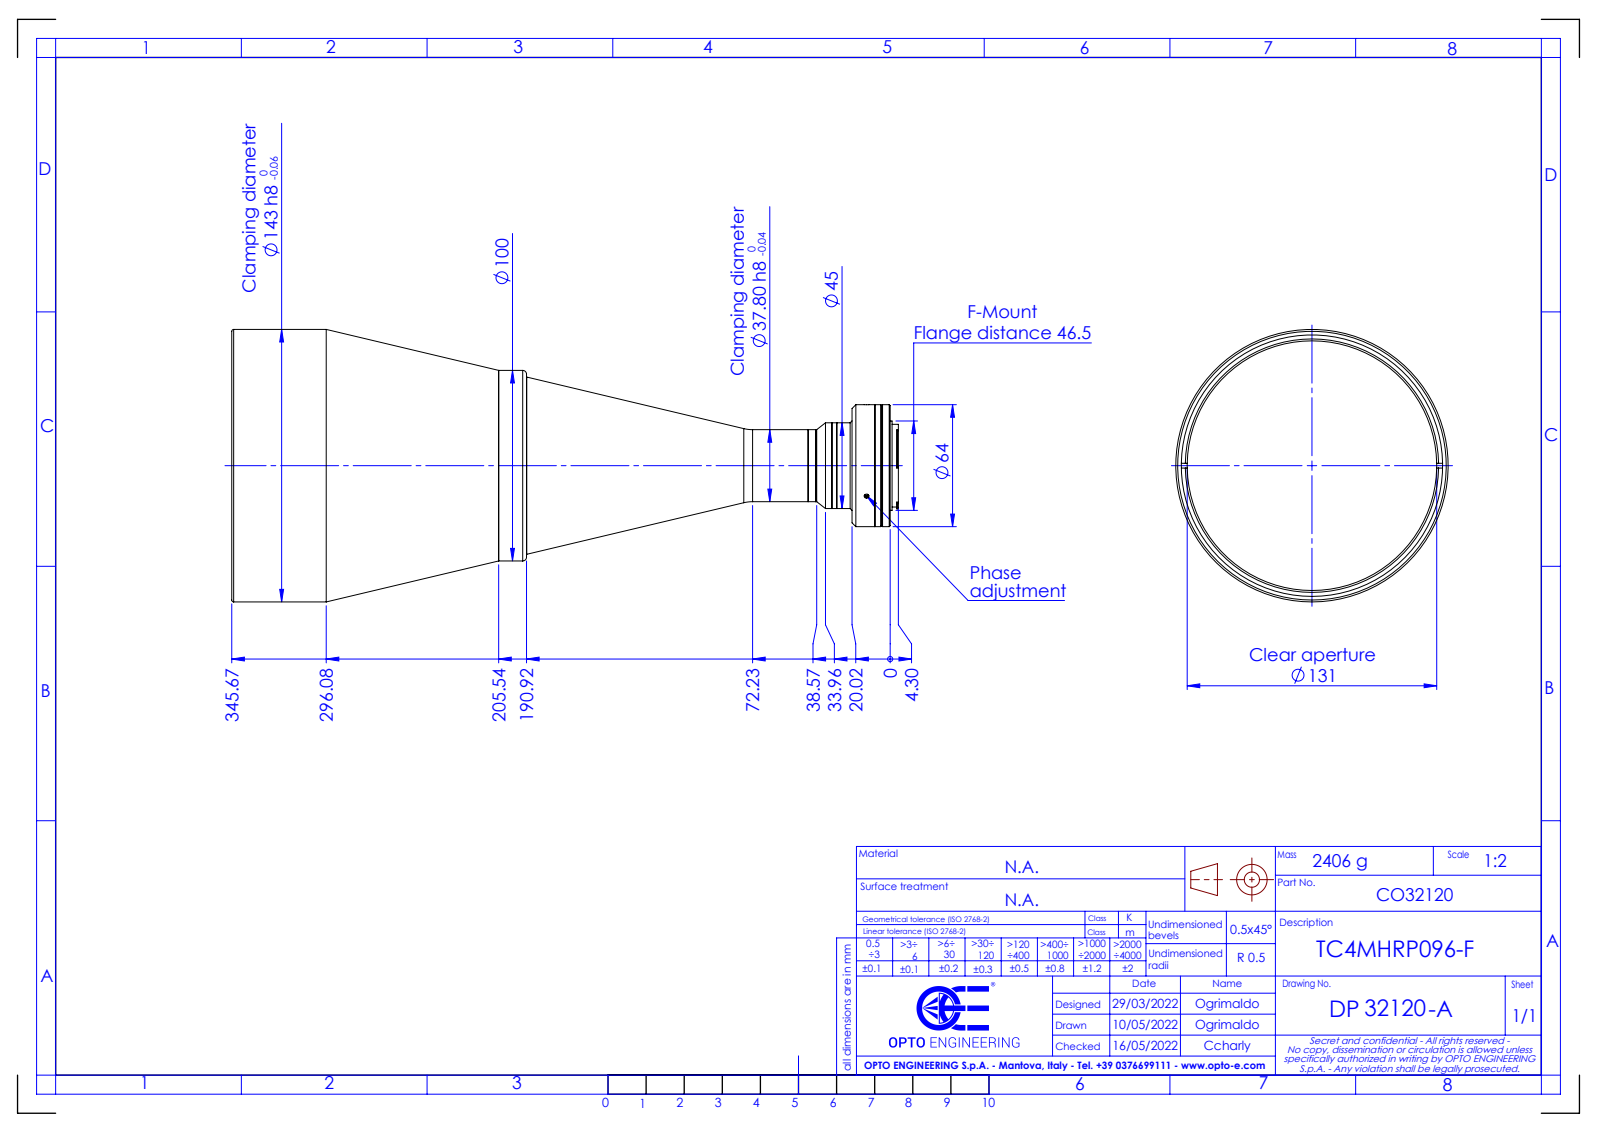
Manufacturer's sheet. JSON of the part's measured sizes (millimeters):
{"part_name": "DP32120-A_TC4MHRP096-F", "step_written_by": "SolidWorks 2021 (CONFIG_CONTROL_DESIGN)", "units": "millimeters", "bodies": {"solids": 0, "faces": 121, "planar": 36, "cylindrical": 53, "other": 32}, "overall_size": [349.97, 143, 143], "round_holes": [[2.5, 1], [29, 1], [32, 1], [42, 1], [131, 1], [137.2, 1]], "round_bosses_or_shafts": [[143, 1], [100, 1], [93, 1], [64, 1], [63.5, 1], [46.9, 1], [45, 1], [43.4, 1]], "partial_cylinders_radius": [[0.5, 2], [1.15, 2], [22.65, 1]], "face_to_face_distances": [139.41, 4, 344.95, 205.54, 5, 1, 339.95, 200.54, 324.93, 185.52]}
